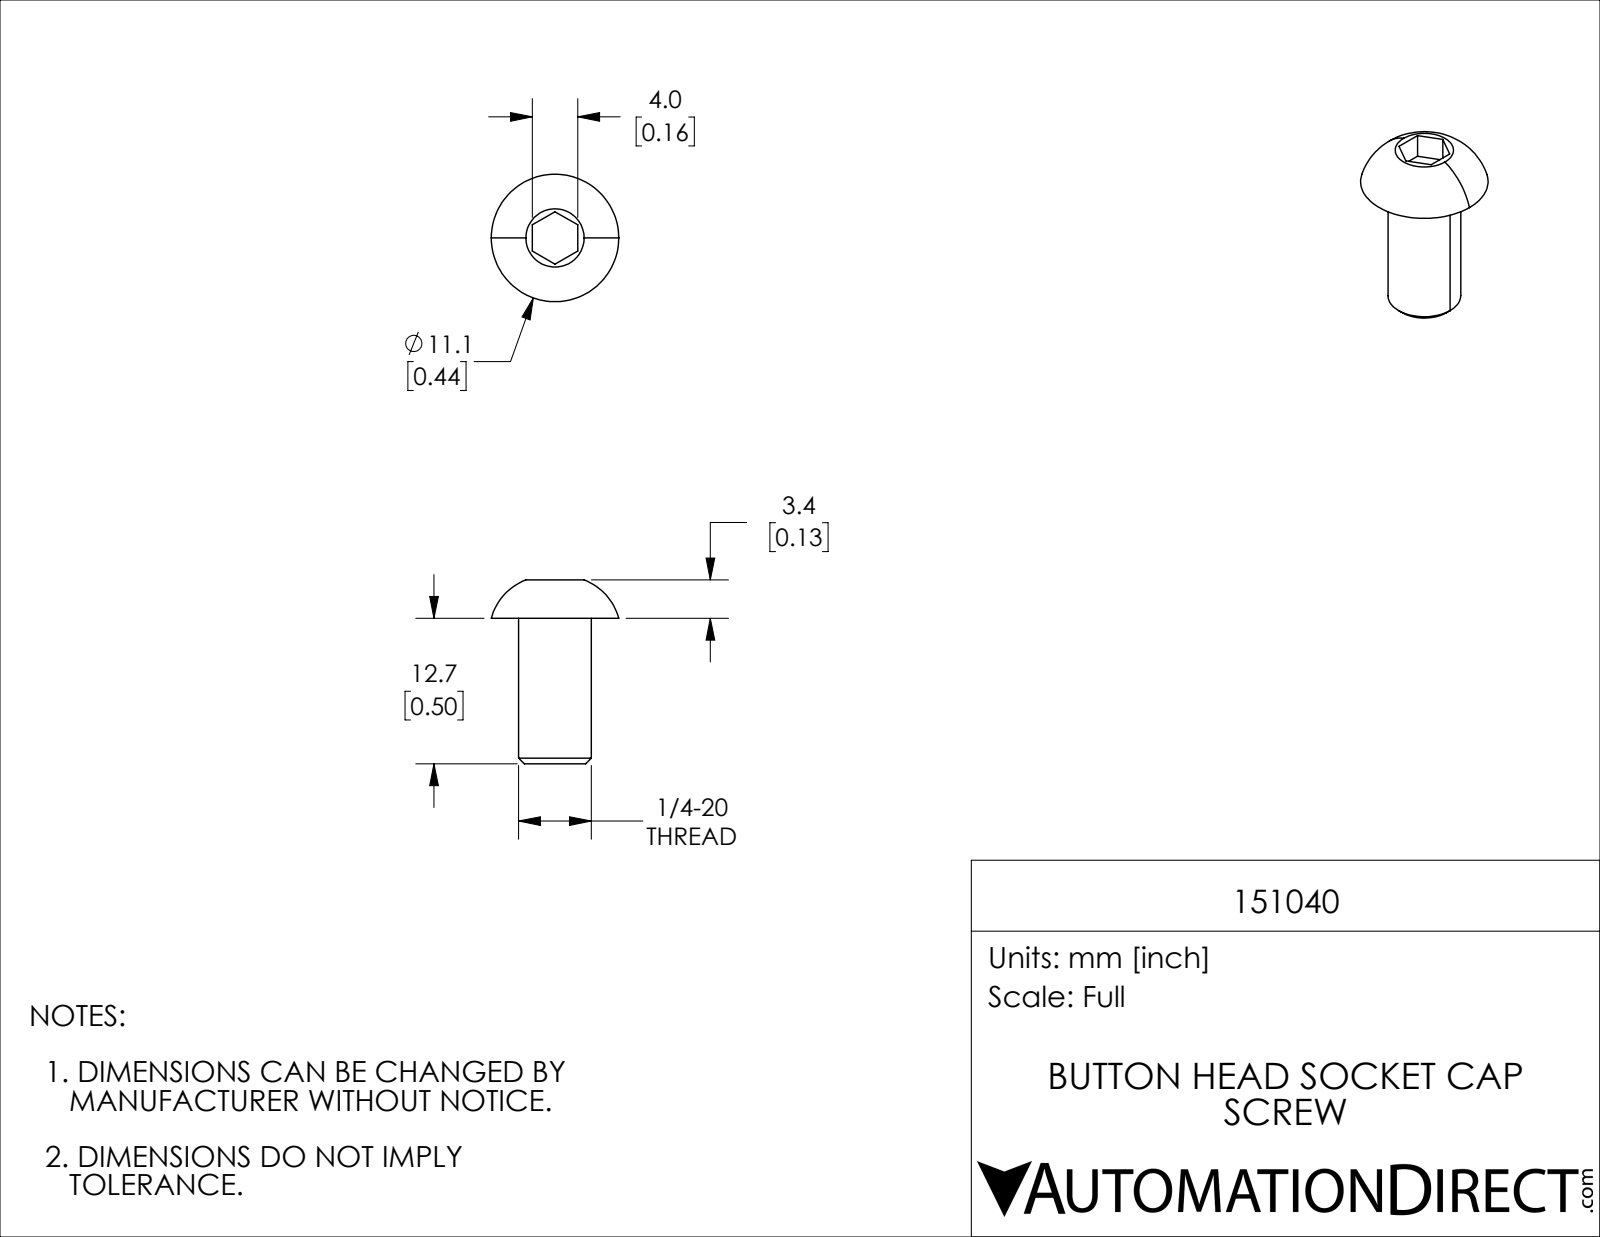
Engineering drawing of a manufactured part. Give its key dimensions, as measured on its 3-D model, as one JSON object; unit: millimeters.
{"part_name": "151040", "step_written_by": "SolidWorks 2021 (CONFIG_CONTROL_DESIGN)", "units": "millimeters", "bodies": {"solids": 1, "faces": 16, "planar": 10, "cylindrical": 2, "other": 4}, "overall_size": [16.05, 11.12, 11.12], "volume_mm3": 594, "surface_area_mm2": 522, "round_bosses_or_shafts": [[6.35, 1]], "face_to_face_distances": [12.7, 3.96, 13.84, 1.14, 16.05, 3.35, 2.21]}
